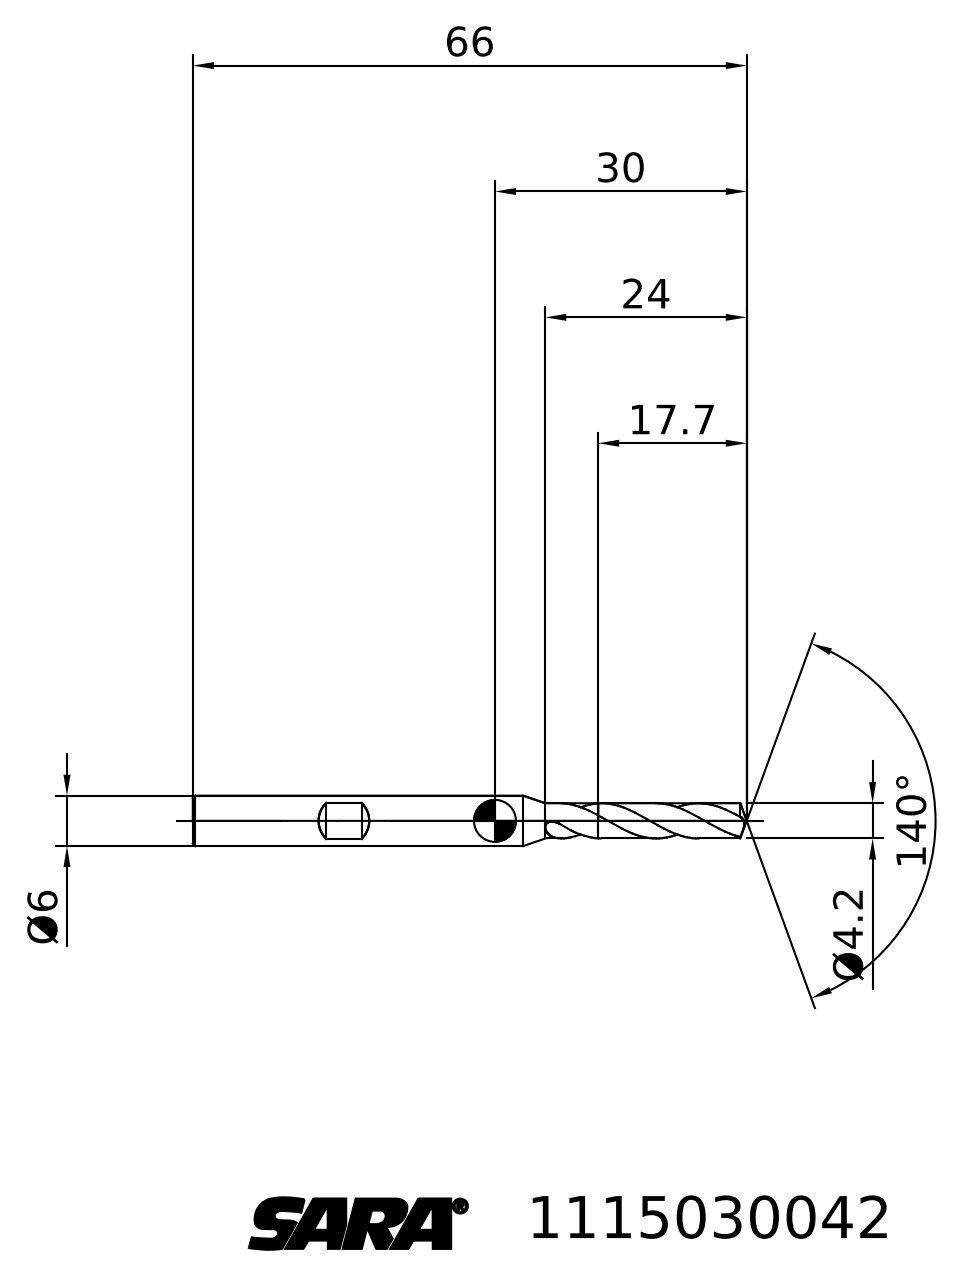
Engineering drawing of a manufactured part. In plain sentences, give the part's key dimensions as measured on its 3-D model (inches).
Its 3-D file was written by "TDM (AUTOMOTIVE_DESIGN)". It is 2 solids with 26 faces: 3 planar, 0 cylindrical and 23 other. Overall it measures 2.598 by 0.236 by 0.236 inches. Its volume is 0.085 cubic inches and its surface area 1.821 square inches. The main face-to-face distances are 1.902.
